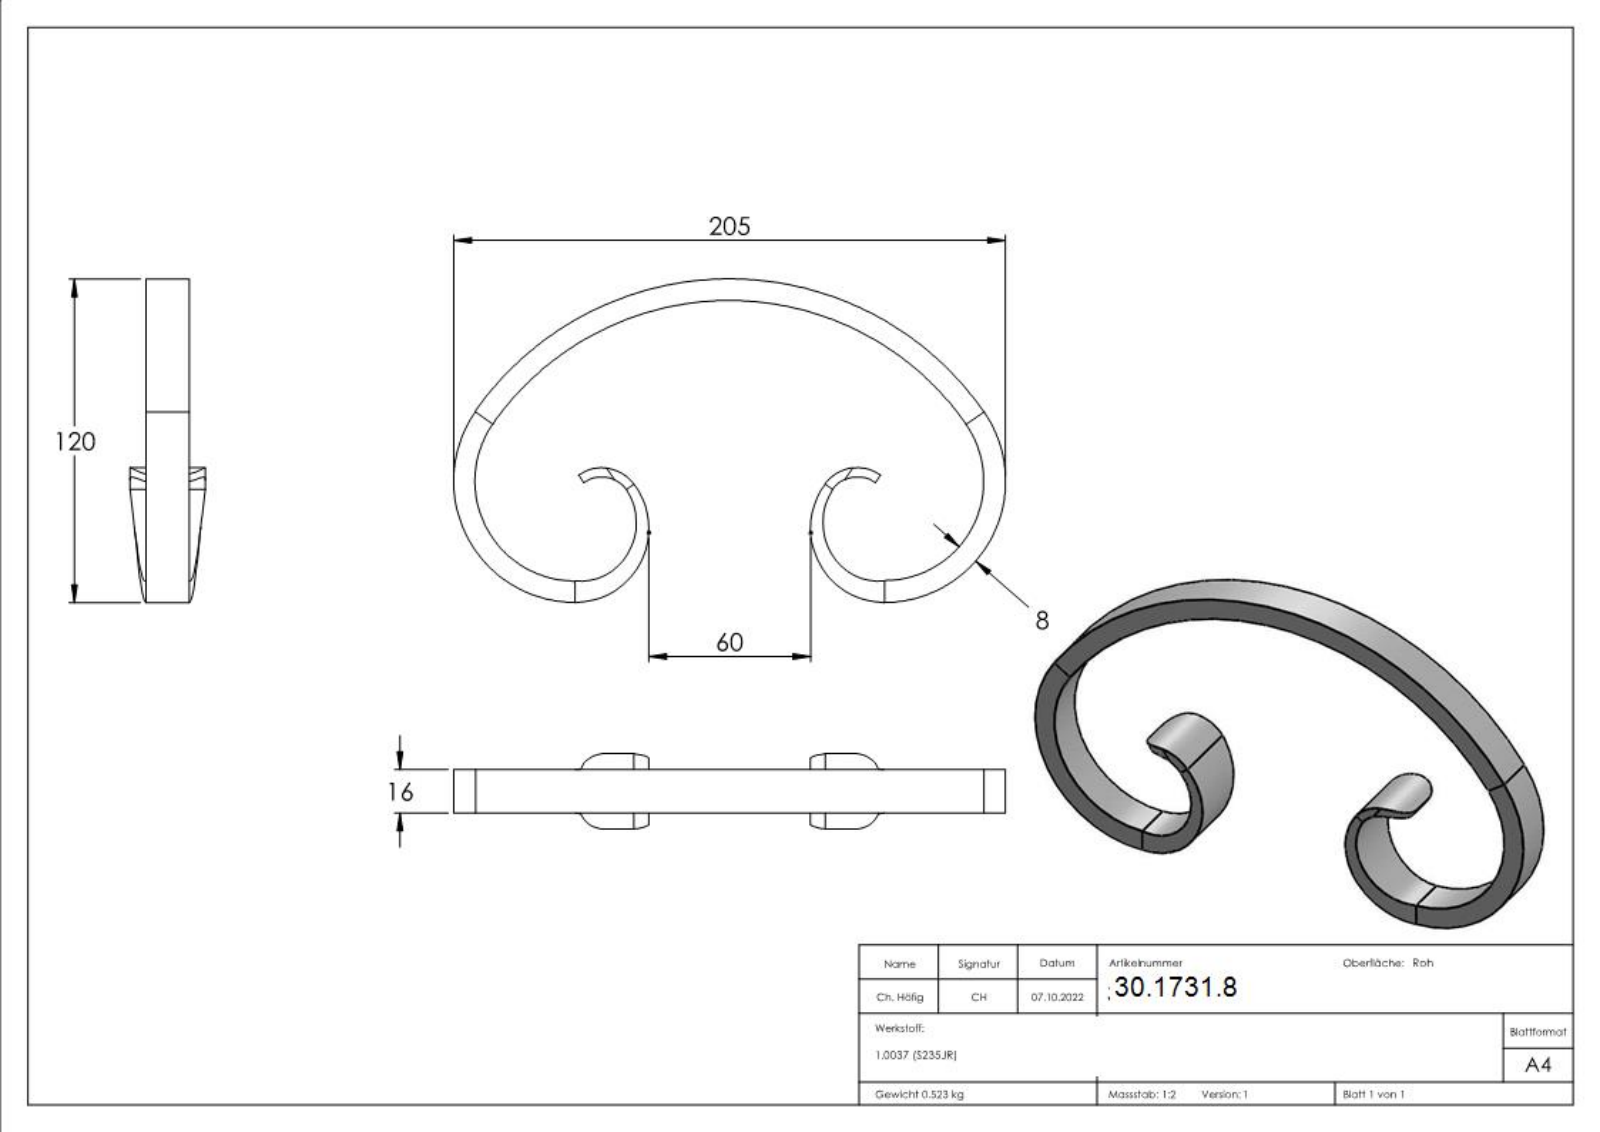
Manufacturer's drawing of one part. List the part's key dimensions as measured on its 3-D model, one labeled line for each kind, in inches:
Part name (STEP PRODUCT): 3082
STEP written by: SolidWorks 2018 (CONFIG_CONTROL_DESIGN)
Units: inches
Bodies: 1 solid, 252 faces (97 planar, 33 cylindrical, 122 other)
Overall size (bounding box): 8.071 × 4.724 × 1.102
Volume: 4.088 in³ · Surface area: 42.55 in²
Partial cylindrical surfaces — rounded edges, fillets, slot ends (radius × count): R0.394 ×4, R0.457 ×2, R0.591 ×2, R1.457 ×2, R1.772 ×2, R4.217 ×1, R4.22 ×1, R4.531 ×1
Main face-to-face distances: 0.63, 0.236, 0.866, 1.102, 0.124, 0.013, 0.551, 0.315, 0.015, 0.072
